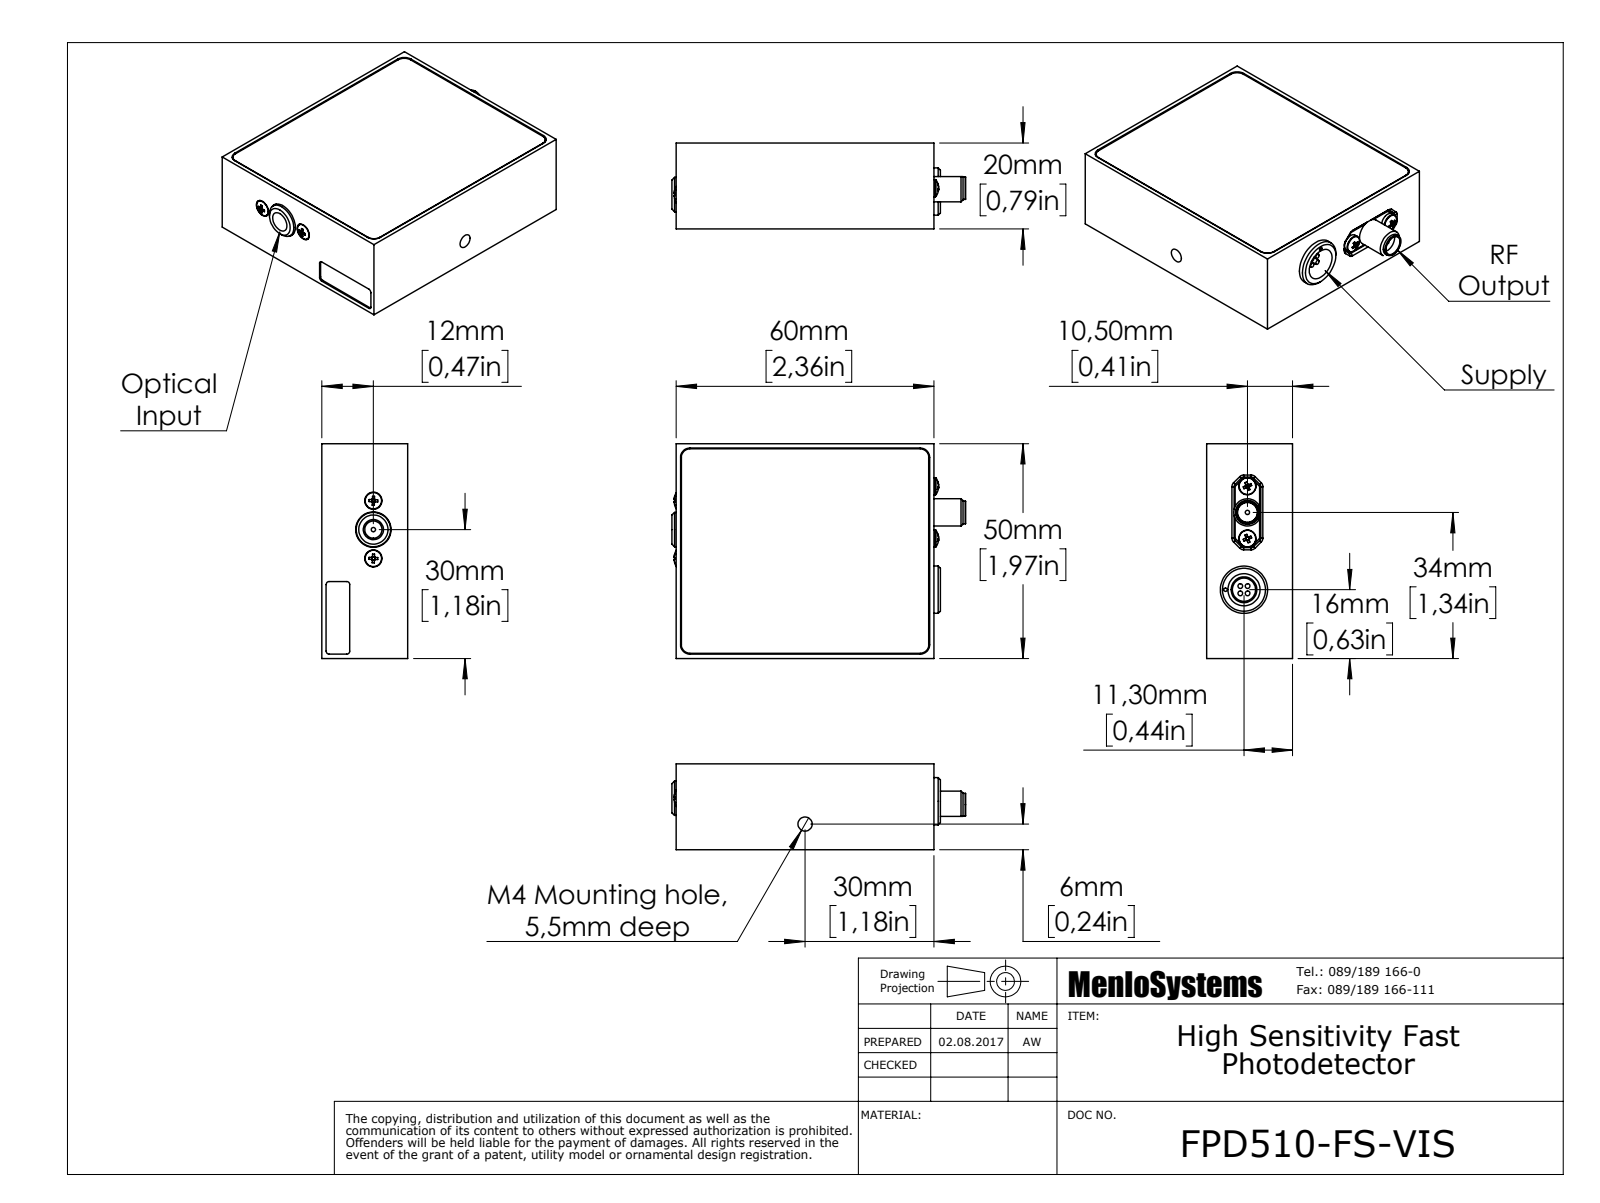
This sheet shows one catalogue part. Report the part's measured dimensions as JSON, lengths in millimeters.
{"part_name": "FPD510-FS-VIS_170721", "step_written_by": "SolidWorks 2016 (AUTOMOTIVE_DESIGN)", "units": "millimeters", "bodies": {"solids": 21, "faces": 989, "planar": 447, "cylindrical": 238, "other": 304}, "overall_size": [68.4, 50, 20], "volume_mm3": 34897, "surface_area_mm2": 22959, "round_holes": [[1.6, 23], [4, 3], [2.6, 2], [0.8, 1], [1, 1], [3.2, 1], [3.3, 1], [4.6, 1], [4.7, 1], [7.5, 1], [8.25, 1], [9.1, 1]], "round_bosses_or_shafts": [[2, 14], [3.8, 12], [1.1, 4], [0.5, 3], [4, 2], [11, 1], [9.6, 1], [9, 1]], "partial_cylinders_radius": [[2.2, 26], [0.7, 8], [0.8, 8], [1.4, 4], [2, 4], [8, 1]], "face_to_face_distances": [0.35, 19.55, 19.9, 6.5, 7, 50, 12.9, 12.55, 1, 43.5], "hole_center_spacings": [4.21, 9.27, 10.5, 14.96, 16.5, 19.36, 20, 21.82]}
